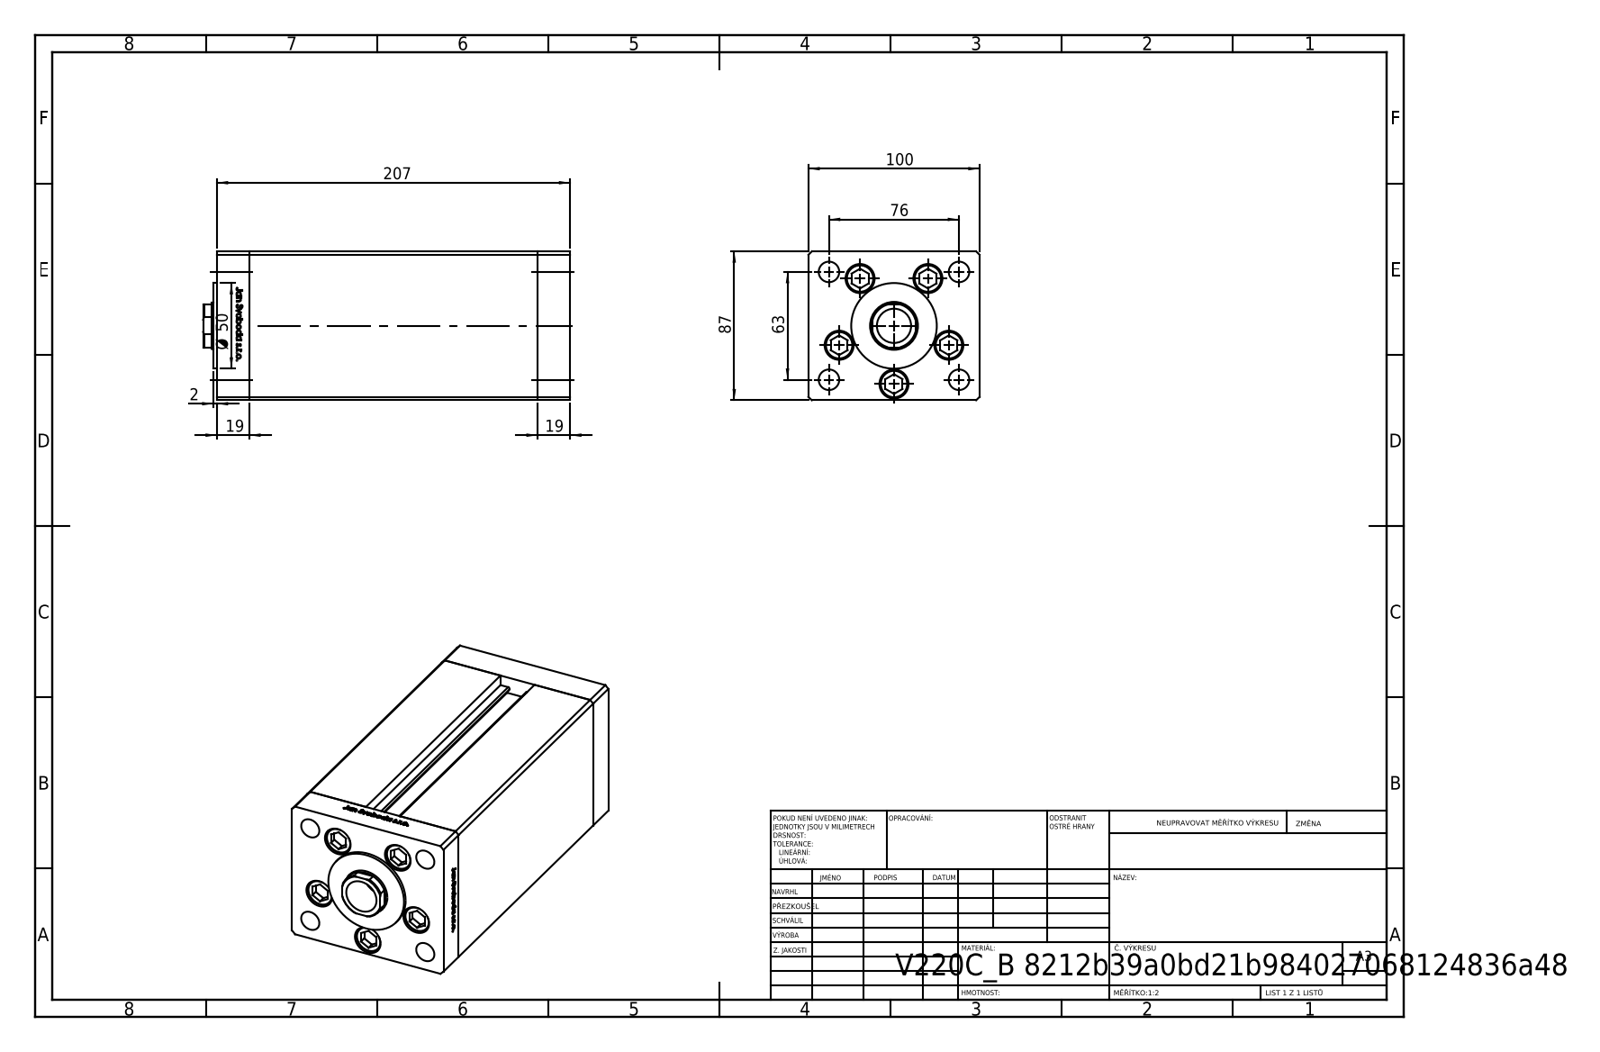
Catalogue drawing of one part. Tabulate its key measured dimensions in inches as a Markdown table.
| quantity | value |
| --- | --- |
| part name | V220C_B MIDDLE; ALLEN BOLT; V220C BACK_B; V220C_B_VC (+1 more) |
| STEP written by | SolidWorks 2019 (CONFIG_CONTROL_DESIGN) |
| units | inches |
| bodies | 14 solids, 1175 faces (460 planar, 143 cylindrical, 572 other) |
| overall size | 8.445 × 3.937 × 3.425 |
| volume | 96.11 in³ |
| surface area | 331.3 in² |
| round holes (diameter × count) | 0.531 × 7, 0.669 × 5, 0.472 × 4, 0.079 × 2, 0.518 × 2, 0.787 × 1, 1.102 × 1 |
| round bosses / shafts (diameter × count) | 0.315 × 5, 0.669 × 2, 1.969 × 1 |
| partial cylindrical surfaces (radius × count) | 0.037 × 2, 0.531 × 1 |
| main face-to-face distances | 3.937, 3.425, 6.634, 0.748, 7.382, 8.13, 0.354, 0.394, 7.776, 7.028 |
| hole center spacings | 1.339, 0.732, 1.561, 1.943, 2.281, 0.828, 1.499, 1.546 |
